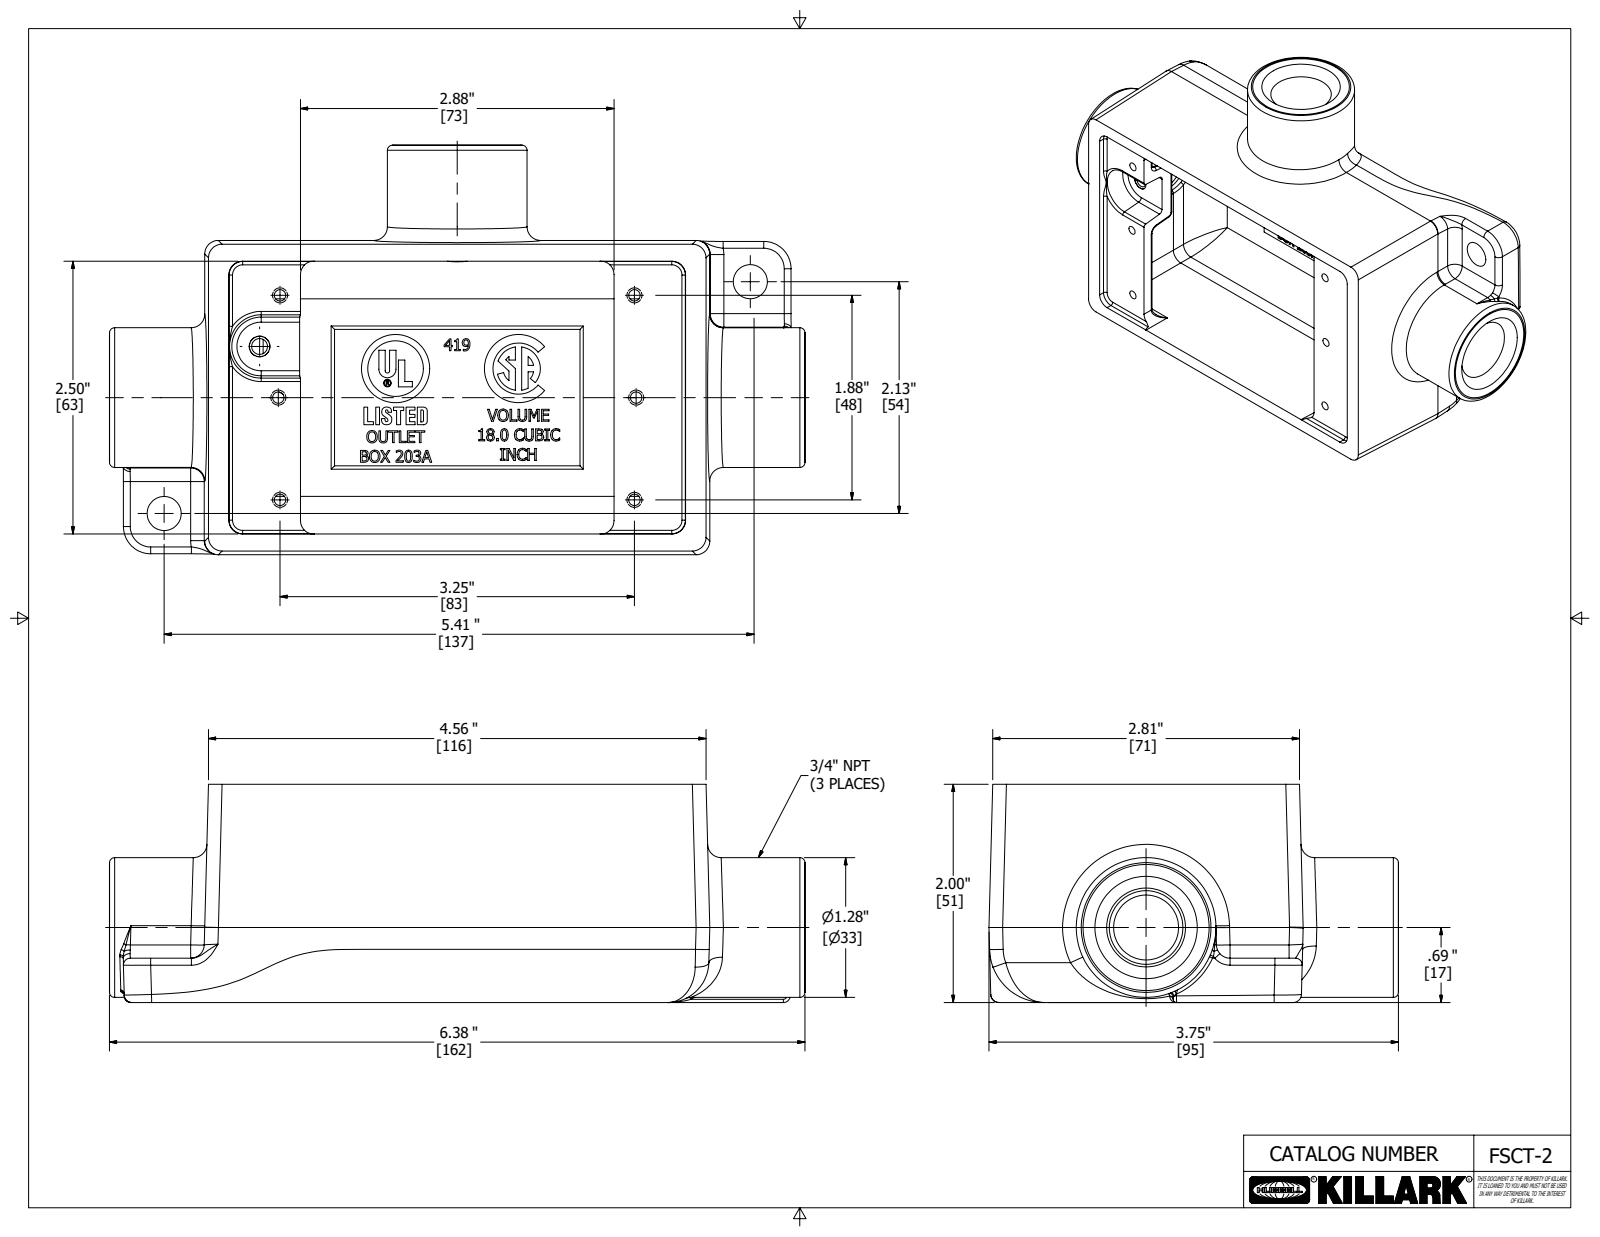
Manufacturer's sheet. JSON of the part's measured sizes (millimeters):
{"part_name": "24550-3", "step_written_by": "Autodesk Inventor 2020 (AUTOMOTIVE_DESIGN)", "units": "millimeters", "bodies": {"solids": 1, "faces": 1167, "planar": 590, "cylindrical": 151, "other": 426}, "overall_size": [162, 95.4, 50.8], "volume_mm3": 156600, "surface_area_mm2": 65610, "round_holes": [[2.6, 6], [15.1, 2], [1.8, 1], [3.7, 1], [15.9, 1]], "round_bosses_or_shafts": [[32.5, 2], [12.9, 1], [1.5, 1]], "partial_cylinders_radius": [[3.2, 37], [0.8, 18], [1.6, 13], [9.5, 4], [0.3, 2], [0.4, 2], [0.9, 2], [1.2, 2]], "face_to_face_distances": [4, 44.5, 69.2, 48.4, 40.5, 4.7, 6.4, 50.8, 46.8, 2.4], "hole_center_spacings": [23.8, 86.3, 47.6, 82.6, 95.3, 3.9, 12.7, 12.8]}
